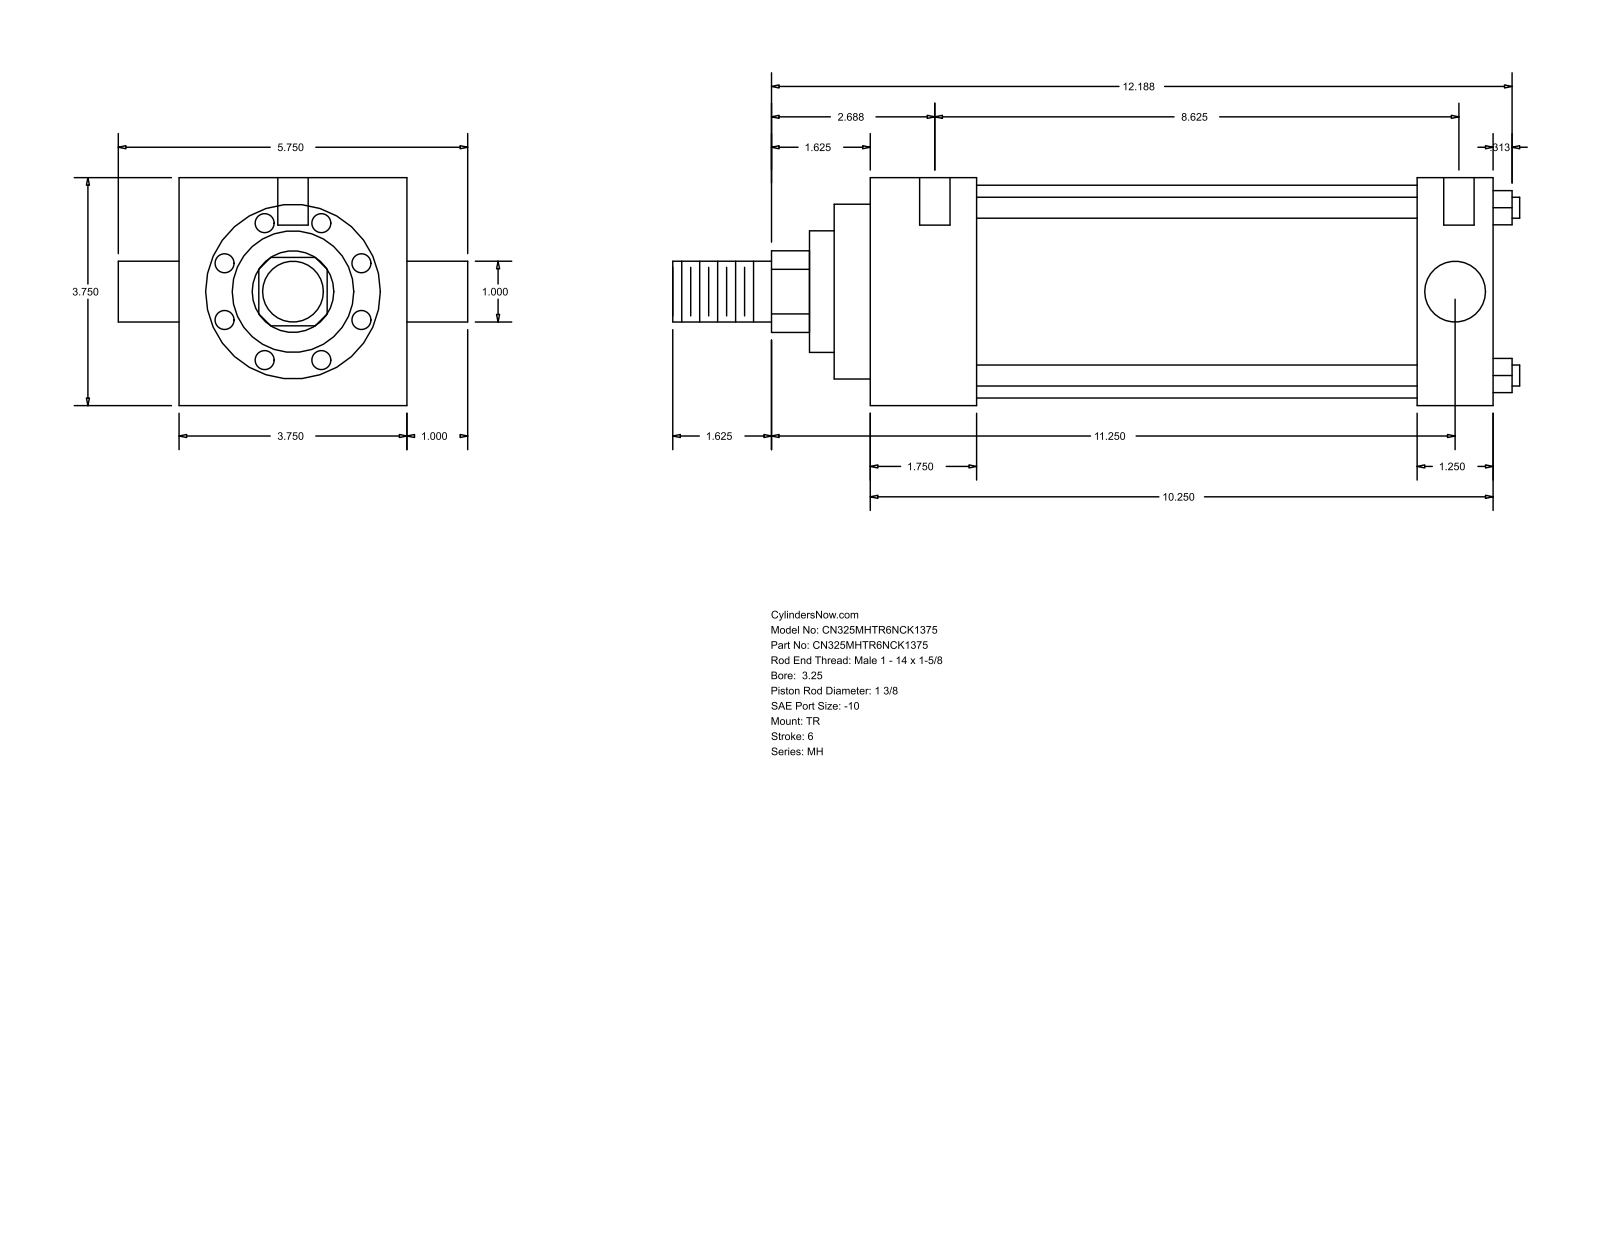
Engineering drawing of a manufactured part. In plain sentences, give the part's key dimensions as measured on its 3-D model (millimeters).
The part is named "MH_TR__0325_1.375". Its 3-D file was written by "GSSL Pune (CONFIG_CONTROL_DESIGN)". It is 0 solids with 86 faces: 61 planar, 25 cylindrical and 0 other. Overall it measures 354.01 by 146.05 by 95.25 millimeters. Round holes: 3 of diameter 5.56, 2 of diameter 12.7. Round bosses or shafts: 4 of diameter 8.76, 2 of diameter 25.4, 1 of diameter 88.9, 1 of diameter 73.03, 1 of diameter 50.8, 1 of diameter 34.92. Partial cylindrical surfaces (rounded edges, fillets, slot ends): 1 of radius 17.06. The main face-to-face distances are 95.24, 260.35, 44.45, 228.61, 184.16, 215.9, 31.74, 15.08, 59.53, 243.69. The hole center spacings are 1.59, 4.76, 219.08, 220.67, 223.84, 225.43.
